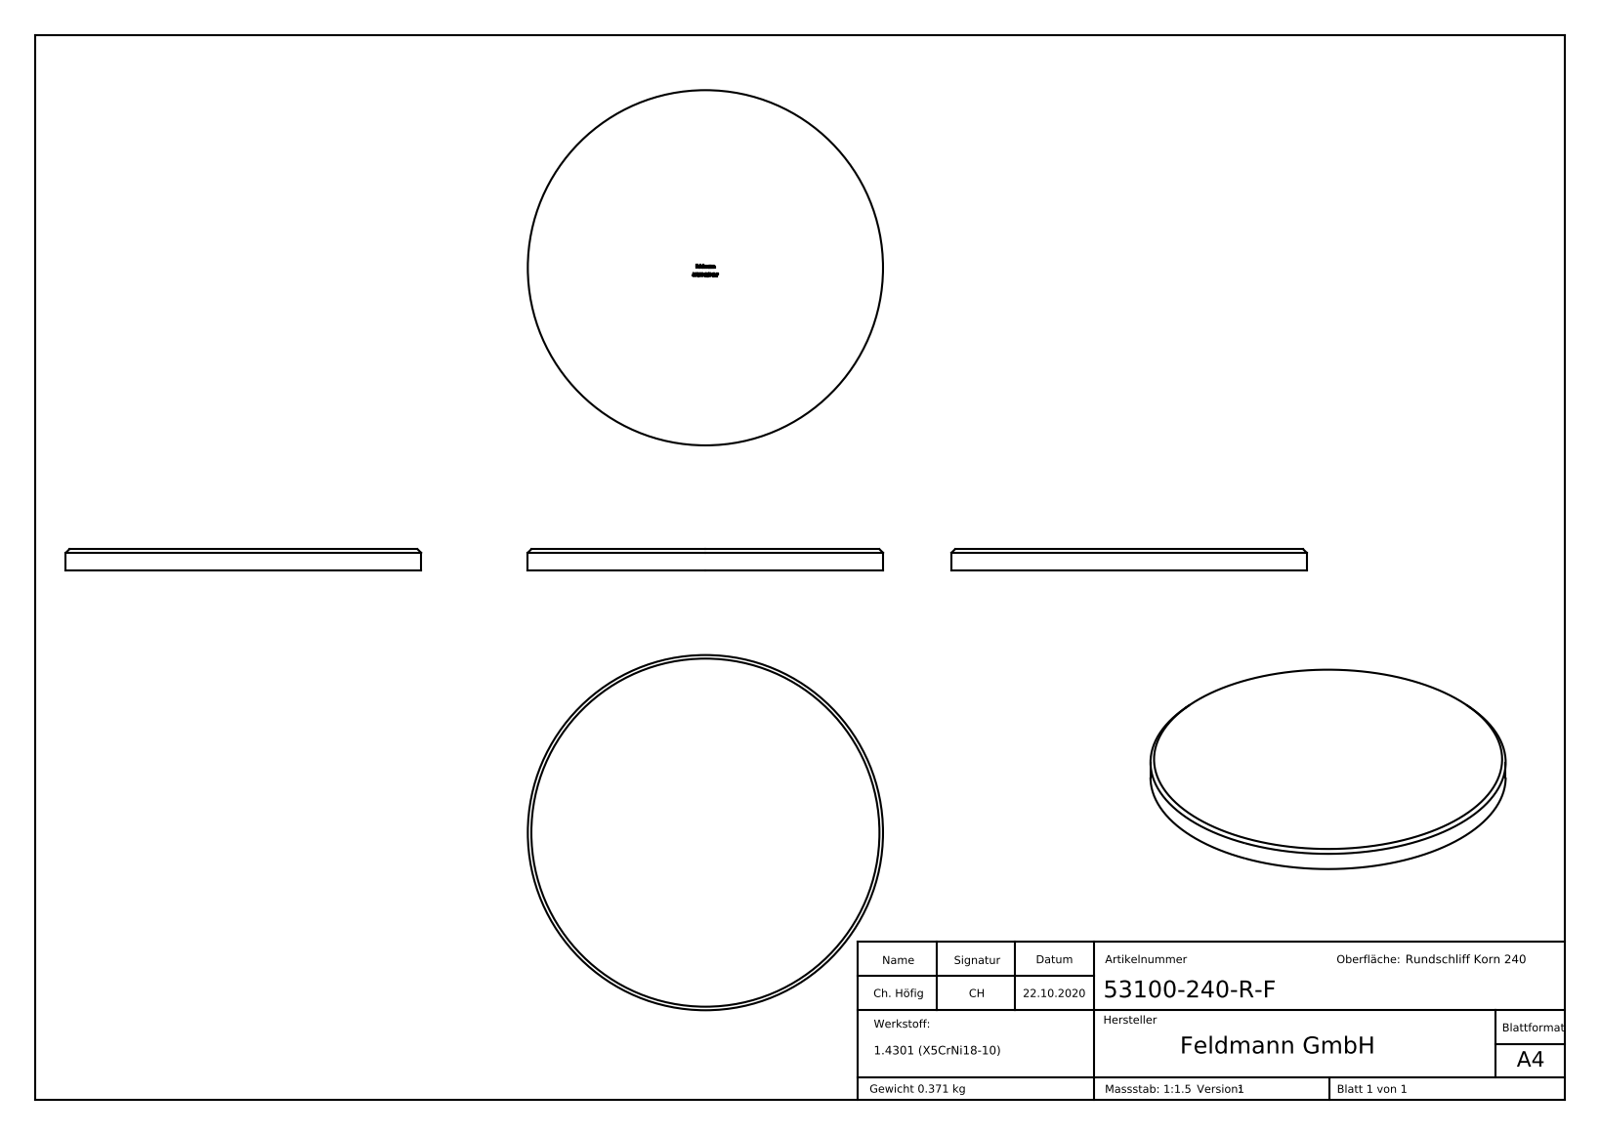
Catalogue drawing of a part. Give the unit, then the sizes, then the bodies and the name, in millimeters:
Units: millimetres
Overall size (bounding box): 100 × 100 × 6
Round bosses / shafts (diameter × count): ⌀100 ×1
Main face-to-face distances: 6, 5.9, 2.32, 1.21, 0.79, 3.49, 0.47, 2.24, 1.78, 0.45
Volume: 46 968 mm³ · Surface area: 17 414 mm²
Bodies: 1 solid, 264 faces (152 planar, 2 cylindrical, 110 other)
Part name (STEP PRODUCT): 53100-240-R-F
STEP written by: SolidWorks 2018 (CONFIG_CONTROL_DESIGN)
